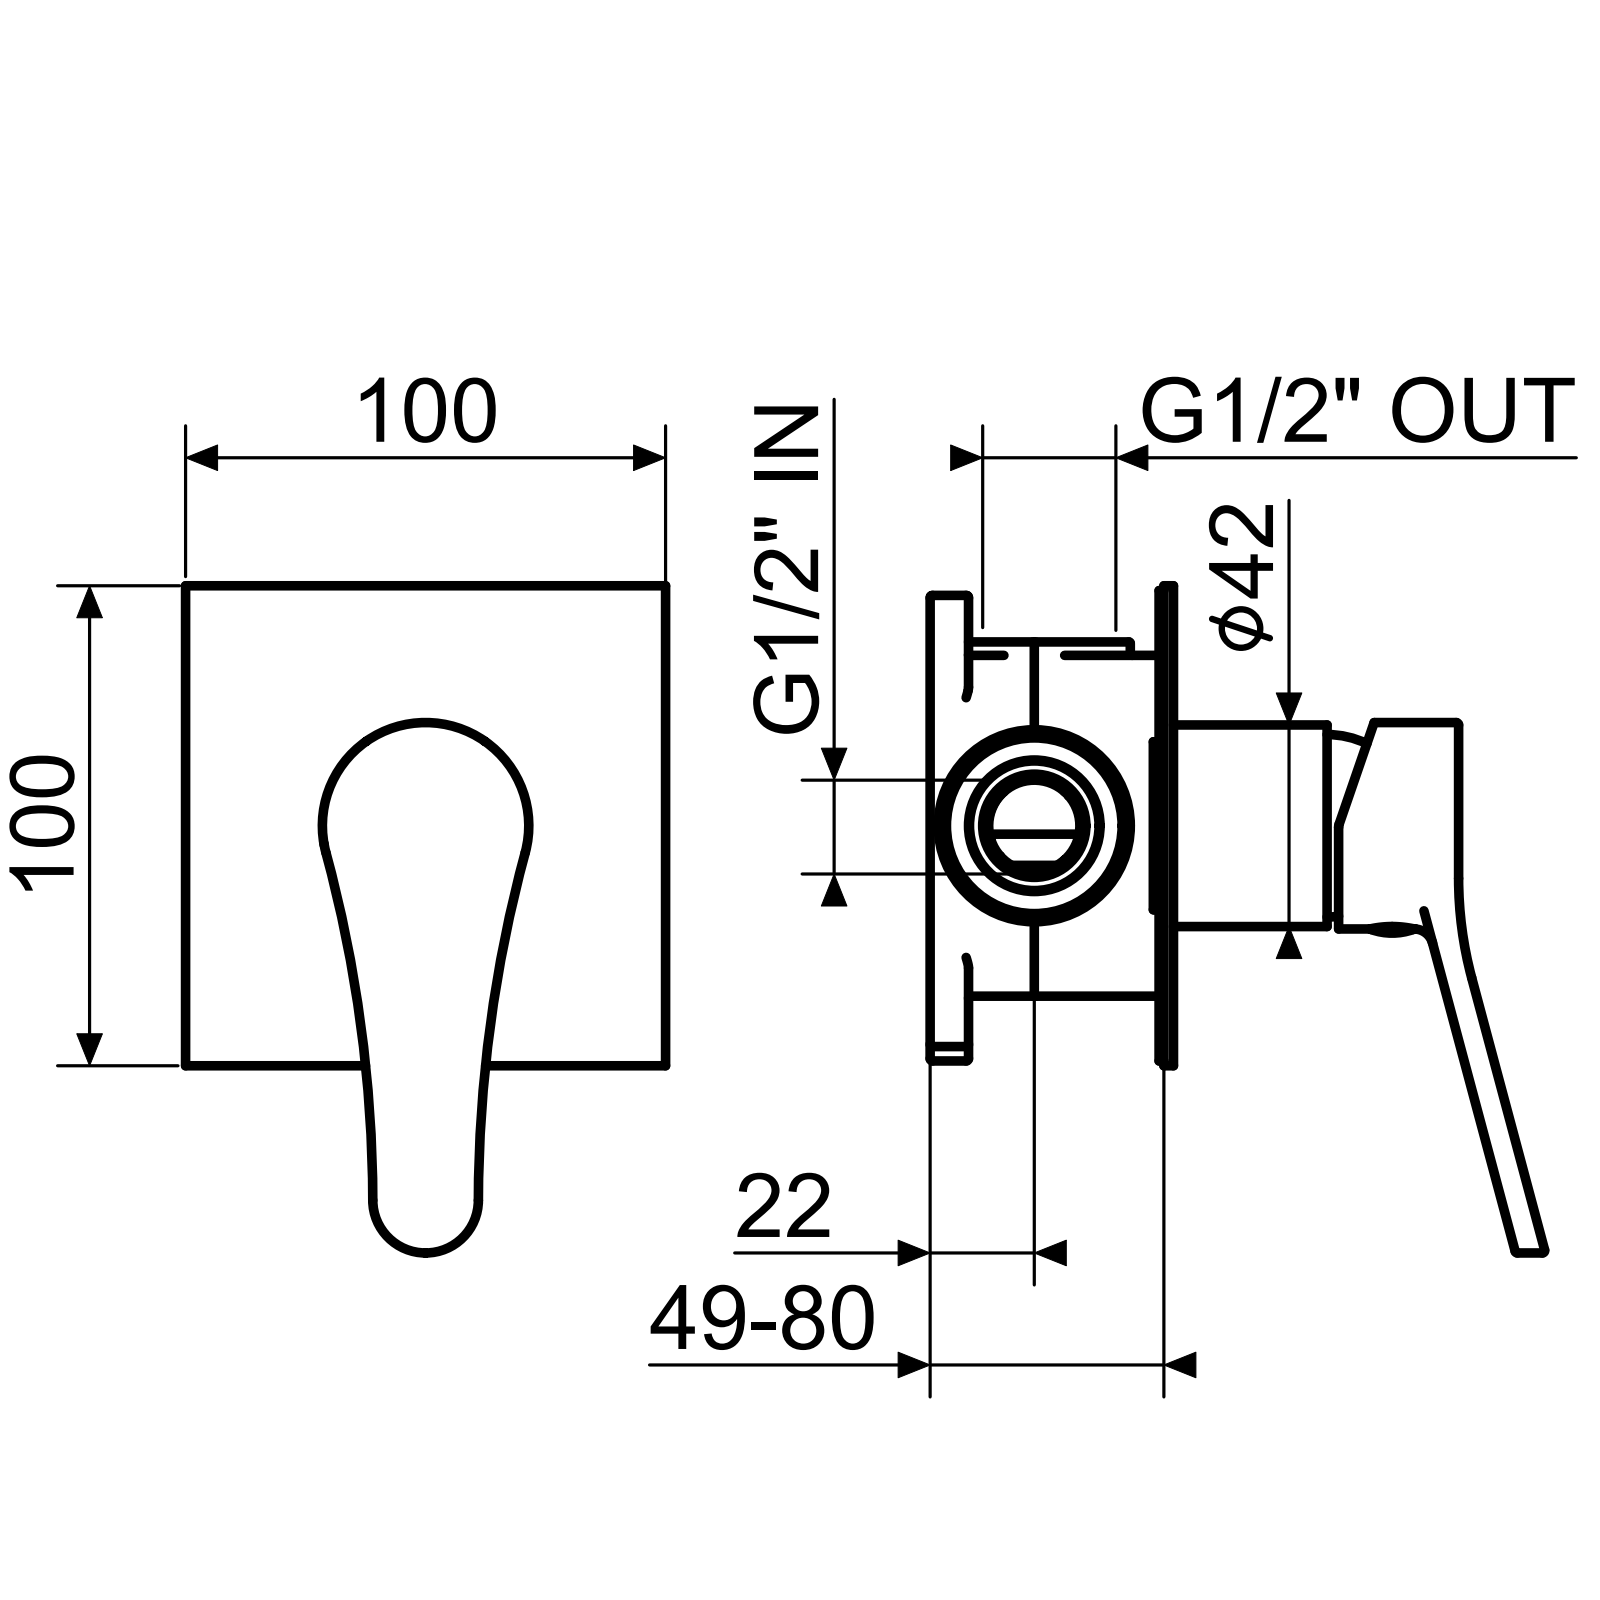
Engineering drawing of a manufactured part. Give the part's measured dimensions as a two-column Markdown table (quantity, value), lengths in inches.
| quantity | value |
| --- | --- |
| part name | SINMAC0008; SCCMAC0005; AKBR005C002; SPLMAC0001 (+4 more) |
| STEP written by | CREO PARAMETRIC BY PTC INC, 2020281 (CONFIG_CONTROL_DESIGN) |
| units | inches |
| bodies | 6 solids, 280 faces (61 planar, 86 cylindrical, 133 other) |
| overall size | 5.472 × 3.937 × 3.348 |
| volume | 2.797 in³ |
| surface area | 74.62 in² |
| round holes (diameter × count) | 0.165 × 1, 0.256 × 1, 0.315 × 1, 1.142 × 1, 1.289 × 1, 1.358 × 1, 1.575 × 1, 1.693 × 1, 1.713 × 1, 1.831 × 1 |
| round bosses / shafts (diameter × count) | 1.929 × 1, 1.654 × 1, 1.339 × 1, 0.197 × 1 |
| partial cylindrical surfaces (radius × count) | 0.02 × 23, 0.039 × 6, 0.063 × 6, 0.012 × 2, 0.059 × 2, 0.118 × 2, 10.766 × 2, 0.1 × 1 |
| main face-to-face distances | 0.079, 2.406, 0.236, 2.484, 2.327, 0.157, 0.236, 2.563, 2.642, 1.79 |
